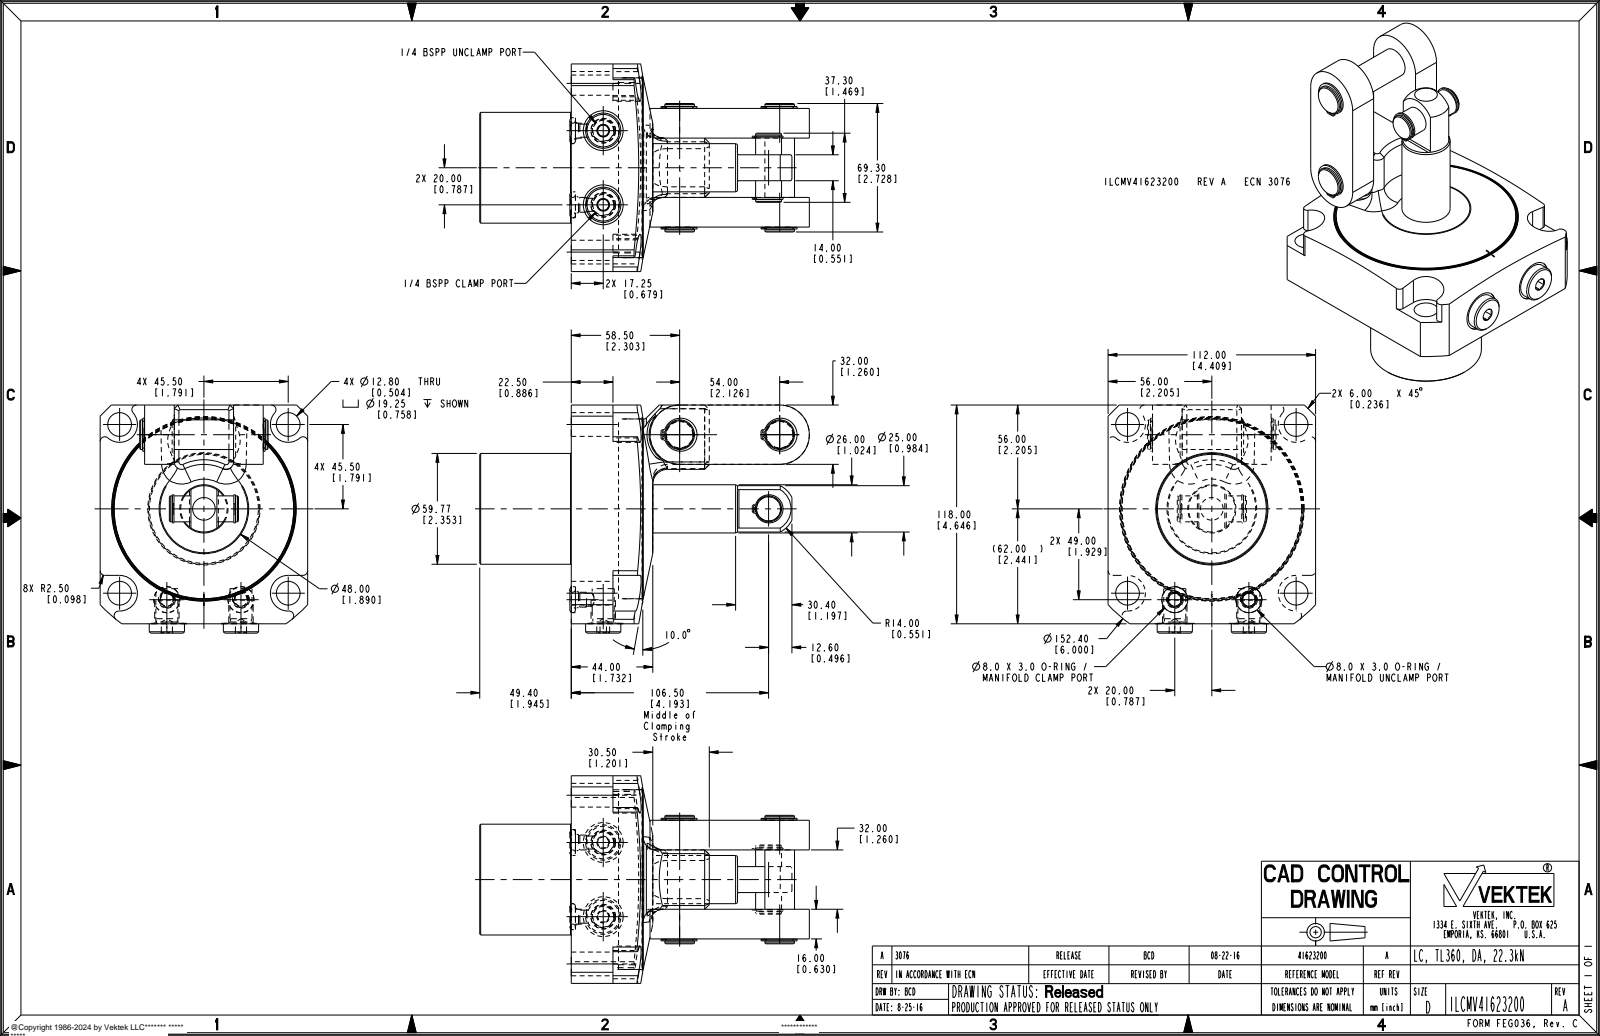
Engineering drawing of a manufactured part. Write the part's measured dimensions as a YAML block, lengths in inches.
part_name: "ILCMV41623200_BODY; ILCMV41623200_LUG; ILCMV41623200"
step_written_by: "PRO/ENGINEER BY PARAMETRIC TECHNOLOGY CORPORATION, 2013320 (AUTOMOTIVE_DESIGN)"
units: inches
bodies: {solids: 4, faces: 407, planar: 142, cylindrical: 173, other: 92}
overall_size: [6.886, 4.844, 4.409]
volume: 48.03
surface_area: 171.7
round_holes:
  - {diameter: 0.047, count: 4}
  - {diameter: 0.504, count: 4}
  - {diameter: 0.047, count: 2}
  - {diameter: 0.277, count: 2}
  - {diameter: 0.468, count: 2}
  - {diameter: 0.551, count: 2}
  - {diameter: 0.579, count: 2}
  - {diameter: 0.846, count: 2}
  - {diameter: 3.82, count: 1}
round_bosses_or_shafts:
  - {diameter: 0.748, count: 2}
  - {diameter: 0.702, count: 2}
  - {diameter: 0.63, count: 2}
  - {diameter: 0.559, count: 2}
  - {diameter: 0.518, count: 2}
  - {diameter: 0.441, count: 2}
  - {diameter: 0.315, count: 2}
  - {diameter: 3.816, count: 1}
partial_cylinders:
  - {radius: 0.098, count: 8}
  - {radius: 0.031, count: 4}
  - {radius: 0.047, count: 4}
  - {radius: 0.05, count: 4}
  - {radius: 0.379, count: 4}
  - {radius: 0.035, count: 2}
  - {radius: 0.047, count: 2}
  - {radius: 0.157, count: 2}
face_to_face_distances: [0.886, 1.004, 0.118, 0.945, 3.465, 0.63, 1.26, 4.409, 1.575, 2.835]
hole_center_spacings: [0.356, 2.533, 3.583, 2.126, 0.122, 1.013, 1.575, 1.777]
